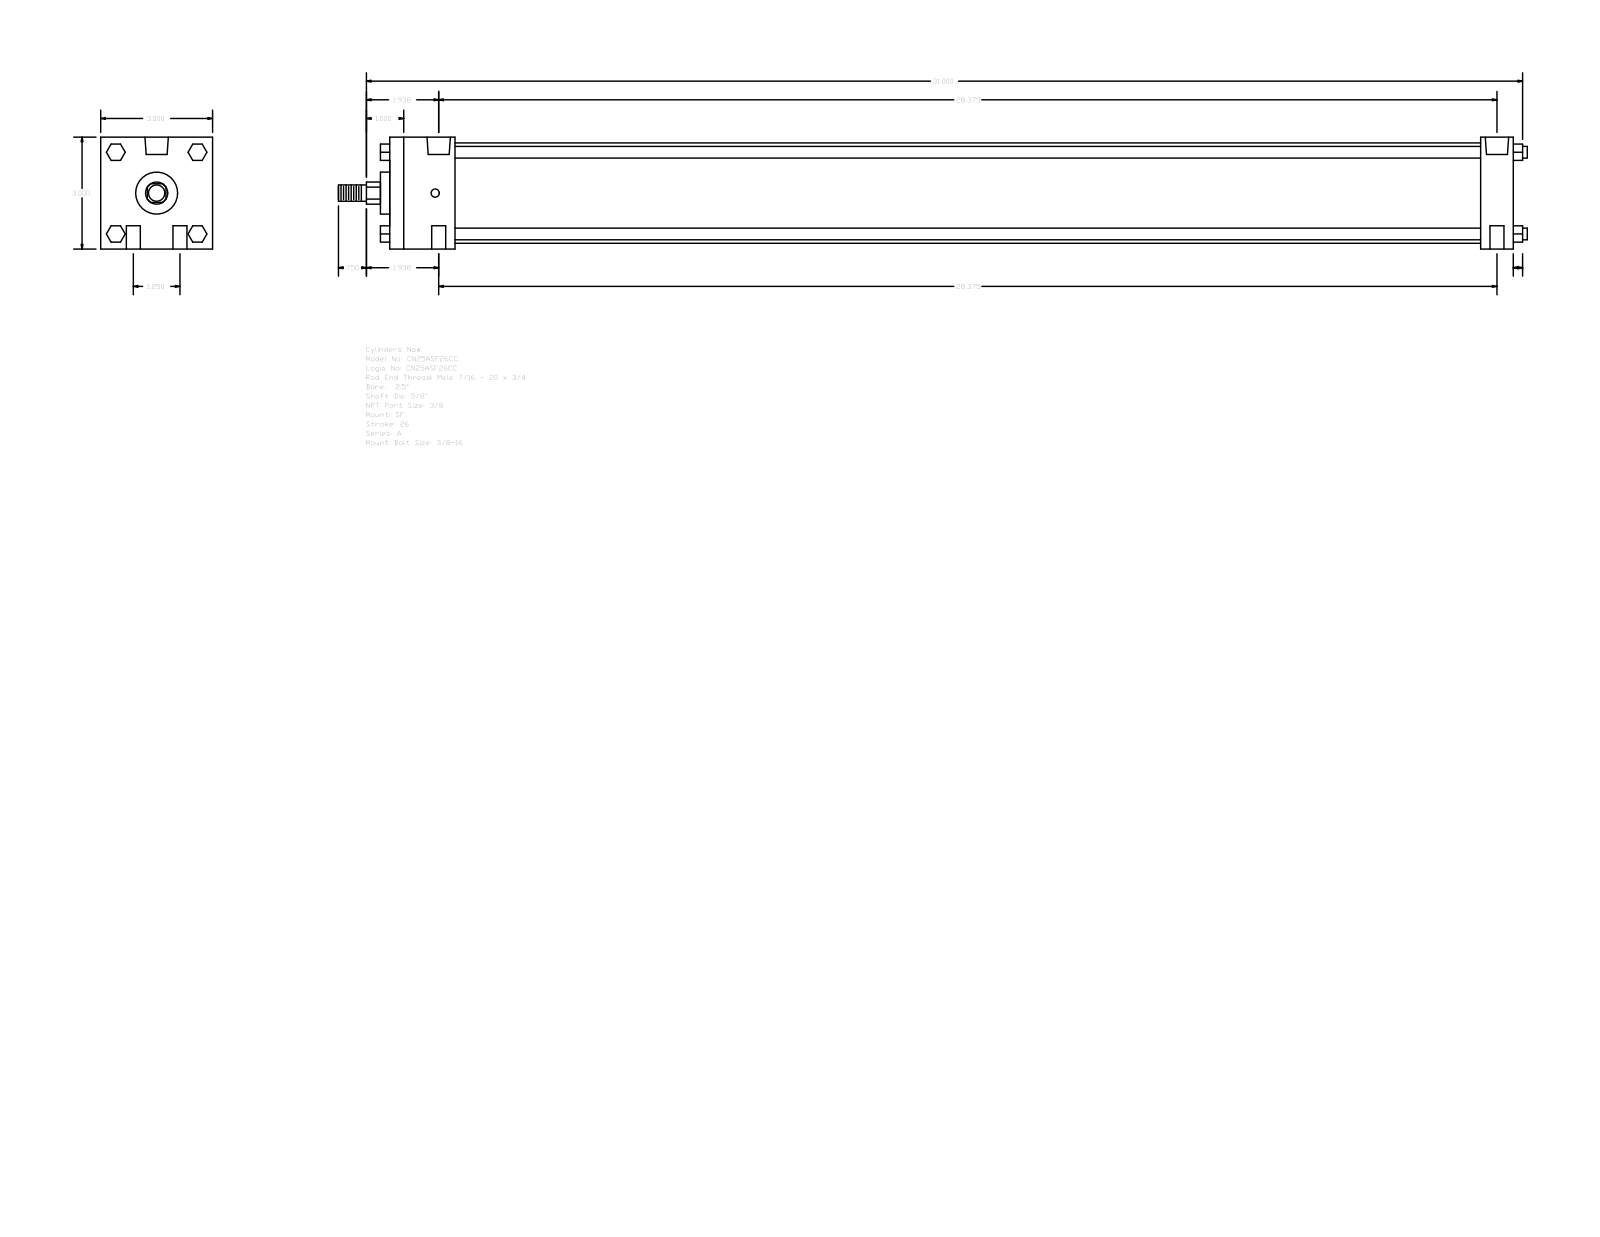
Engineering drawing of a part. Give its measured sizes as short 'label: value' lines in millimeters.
name: A_SF__0250_0.625
written by: GSSL Pune (CONFIG_CONTROL_DESIGN)
unit: mm
bodies: 0 solids, 124 faces (94 planar, 30 cylindrical, 0 other)
size: 809.62 × 76.2 × 76.2
holes: 4× ⌀9.53, 2× ⌀5.56, 2× ⌀15.93
bosses: 4× ⌀7.94, 1× ⌀68.33, 1× ⌀28.57, 1× ⌀15.88, 1× ⌀11.11
rounds: 1× R7.54
face distances: 76.2, 765.17, 44.45, 742.95, 22.22, 698.5, 720.72, 6.35, 771.52, 50.8
hole spacings: 15.88, 720.9, 720.73, 31.76, 721.43, 725.49
